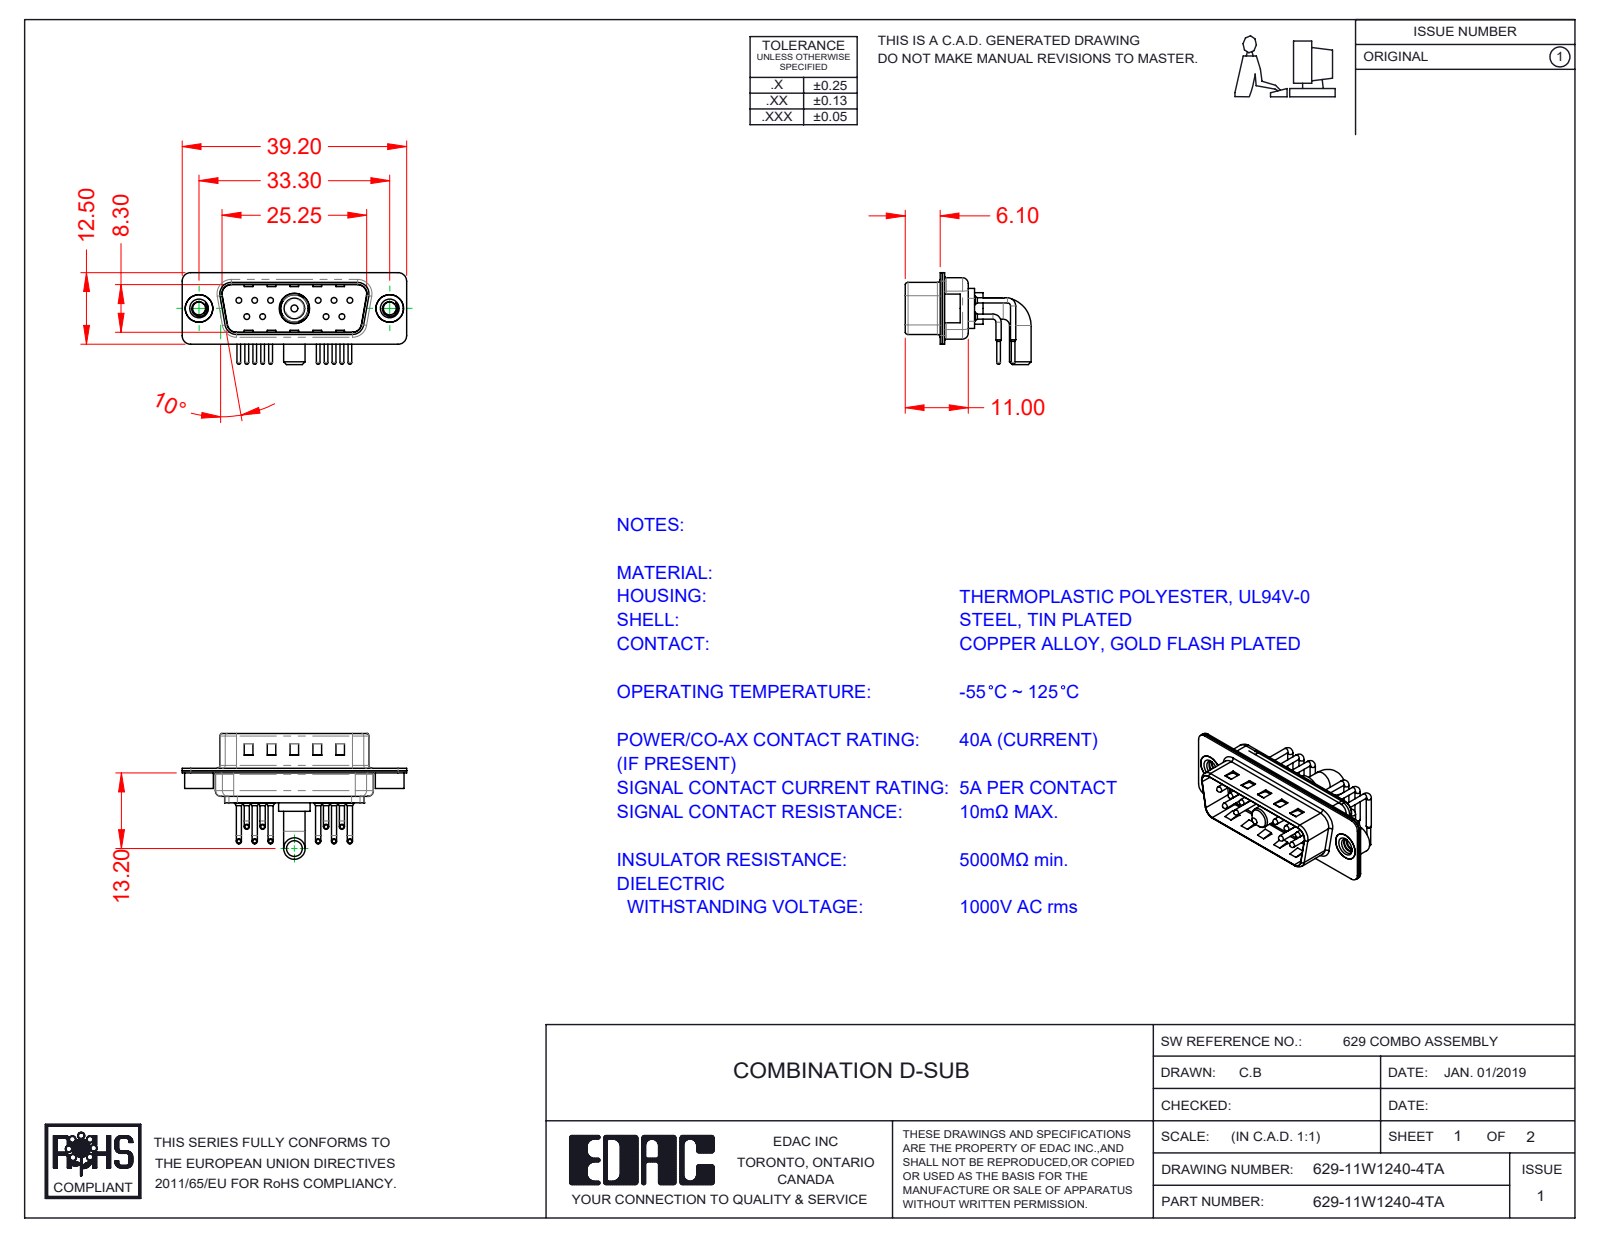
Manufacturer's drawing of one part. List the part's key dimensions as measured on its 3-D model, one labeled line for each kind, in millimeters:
Part name (STEP PRODUCT): 629Combo Contact Row 2; 629Combo Contact Row 1; 629Combo Shell Rear_15 Contacts; 629-11W1240-4TA (+4 more)
STEP written by: SolidWorks 2020 (CONFIG_CONTROL_DESIGN)
Units: millimetres
Bodies: 17 solids, 1496 faces (798 planar, 518 cylindrical, 180 other)
Overall size (bounding box): 39.2 × 21.98 × 16.05
Volume: 2 137 mm³ · Surface area: 5 277 mm²
Round holes (diameter × count): ⌀0.75 ×10, ⌀1.6 ×10, ⌀2 ×10, ⌀2.26 ×2, ⌀4 ×2, ⌀4.8 ×2, ⌀4.85 ×1, ⌀5.3 ×1
Round bosses / shafts (diameter × count): ⌀0.9 ×20, ⌀1.5 ×10, ⌀1 ×10, ⌀0.65 ×10, ⌀5 ×2, ⌀4.9 ×2, ⌀3.75 ×2, ⌀5.5 ×1
Partial cylindrical surfaces — rounded edges, fillets, slot ends (radius × count): R1.5 ×16, R2 ×12, R1.01 ×10, R0.5 ×8, R1.6 ×8, R1 ×7, R0.25 ×4, R0.6 ×4
Main face-to-face distances: 0.4, 0.8, 9.5, 9.1, 8.7, 9.9, 0.75, 1.2, 5.6, 0.35
Hole centre spacings: 3.16, 2.77, 13.85, 11.08, 16.62, 5.03, 5.04, 5.54
